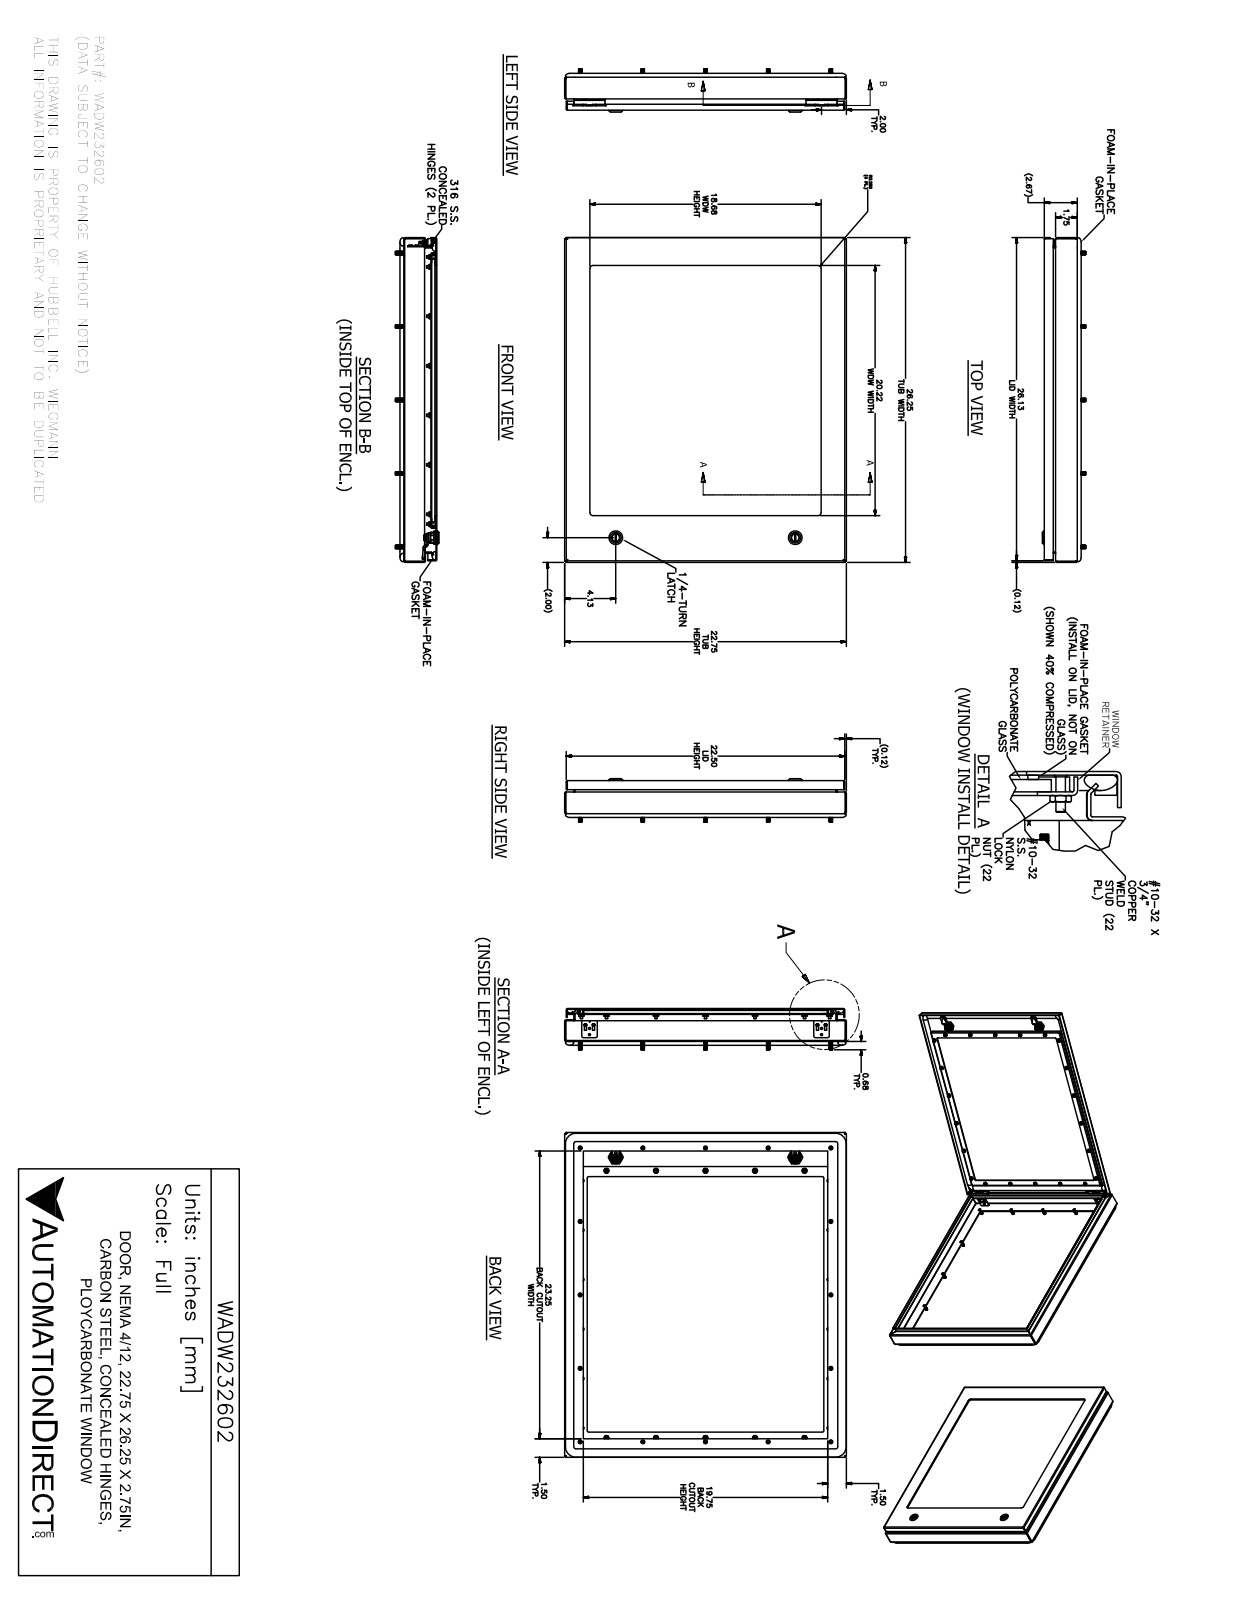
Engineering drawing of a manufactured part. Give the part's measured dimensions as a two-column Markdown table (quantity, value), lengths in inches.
| quantity | value |
| --- | --- |
| part name | WADW232602 |
| STEP written by | SolidWorks 2017 (AUTOMOTIVE_DESIGN) |
| units | inches |
| bodies | 100 solids, 2698 faces (1046 planar, 818 cylindrical, 834 other) |
| overall size | 26.25 × 22.75 × 3.475 |
| volume | 199.9 in³ |
| surface area | 2 834 in² |
| round holes (diameter × count) | 0.156 × 24, 0.281 × 22, 0.249 × 15, 0.093 × 4, 0.152 × 4, 0.167 × 4, 0.172 × 4, 0.188 × 4, 0.197 × 2, 0.315 × 2, 0.394 × 2, 0.402 × 2 |
| round bosses / shafts (diameter × count) | 0.25 × 30, 0.19 × 22, 0.36 × 4, 0.32 × 4, 0.256 × 4, 0.164 × 4, 0.131 × 4, 1.102 × 2 |
| partial cylindrical surfaces (radius × count) | 0.012 × 54, 0.031 × 34, 0.05 × 26, 0.105 × 24, 0.02 × 23, 0.125 × 20, 0.016 × 18, 0.032 × 8 |
| main face-to-face distances | 0.074, 0.25, 0.337, 0.087, 0.411, 2.593, 0.161, 2.182, 2.432, 2.519 |
| hole center spacings | 4, 8, 12, 20.45, 21.591, 21.962, 16, 20.055 |
